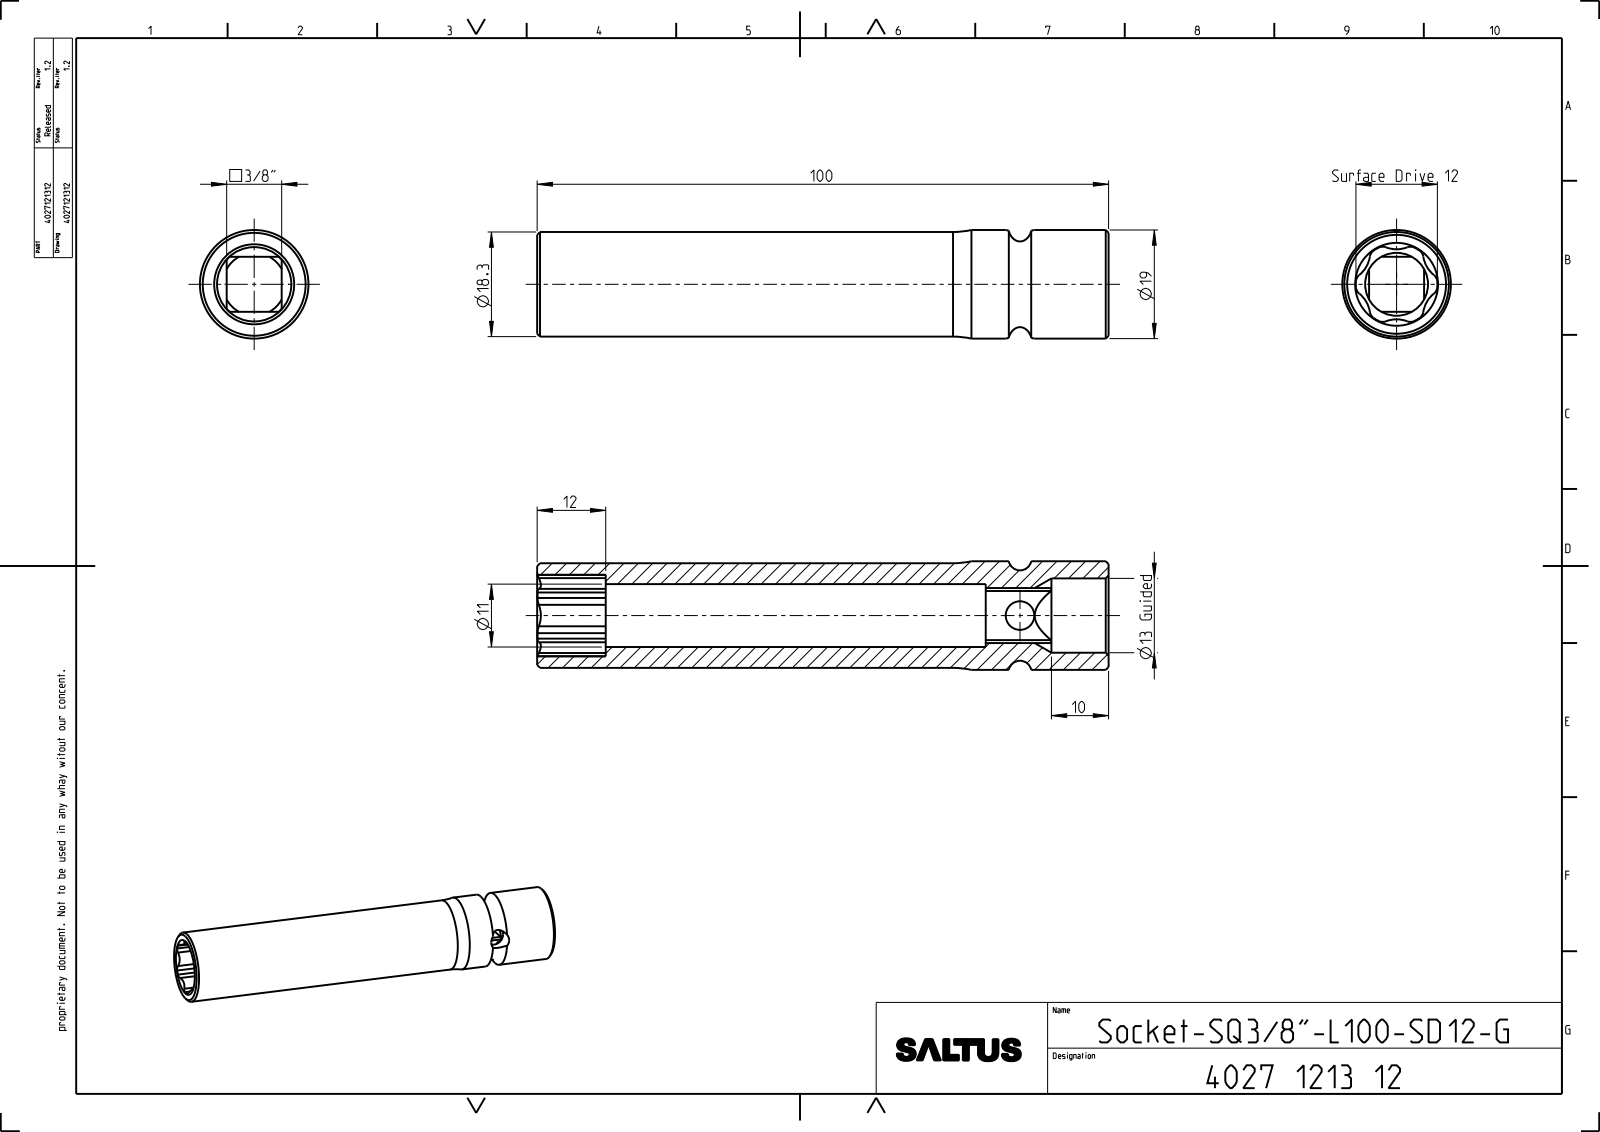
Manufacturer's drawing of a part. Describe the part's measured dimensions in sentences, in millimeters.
The part is named "4027121312". Its 3-D file was written by "CREO PARAMETRIC BY PTC INC, 2022414 (CONFIG_CONTROL_DESIGN)". It is 1 solid with 71 faces: 15 planar, 42 cylindrical and 14 other. Overall it measures 100 by 19 by 19 millimeters. Its volume is 15 965 cubic millimeters and its surface area 9 856 square millimeters. Round holes: 1 of diameter 5, 1 of diameter 11, 1 of diameter 13. Round bosses or shafts: 1 of diameter 19, 1 of diameter 18.3. Partial cylindrical surfaces (rounded edges, fillets, slot ends): 12 of radius 1.5, 6 of radius 5.1, 1 of radius 6.45, 1 of radius 7.13. The main face-to-face distances are 9.62, 100, 88, 12, 21.5, 66.5, 78.5.
